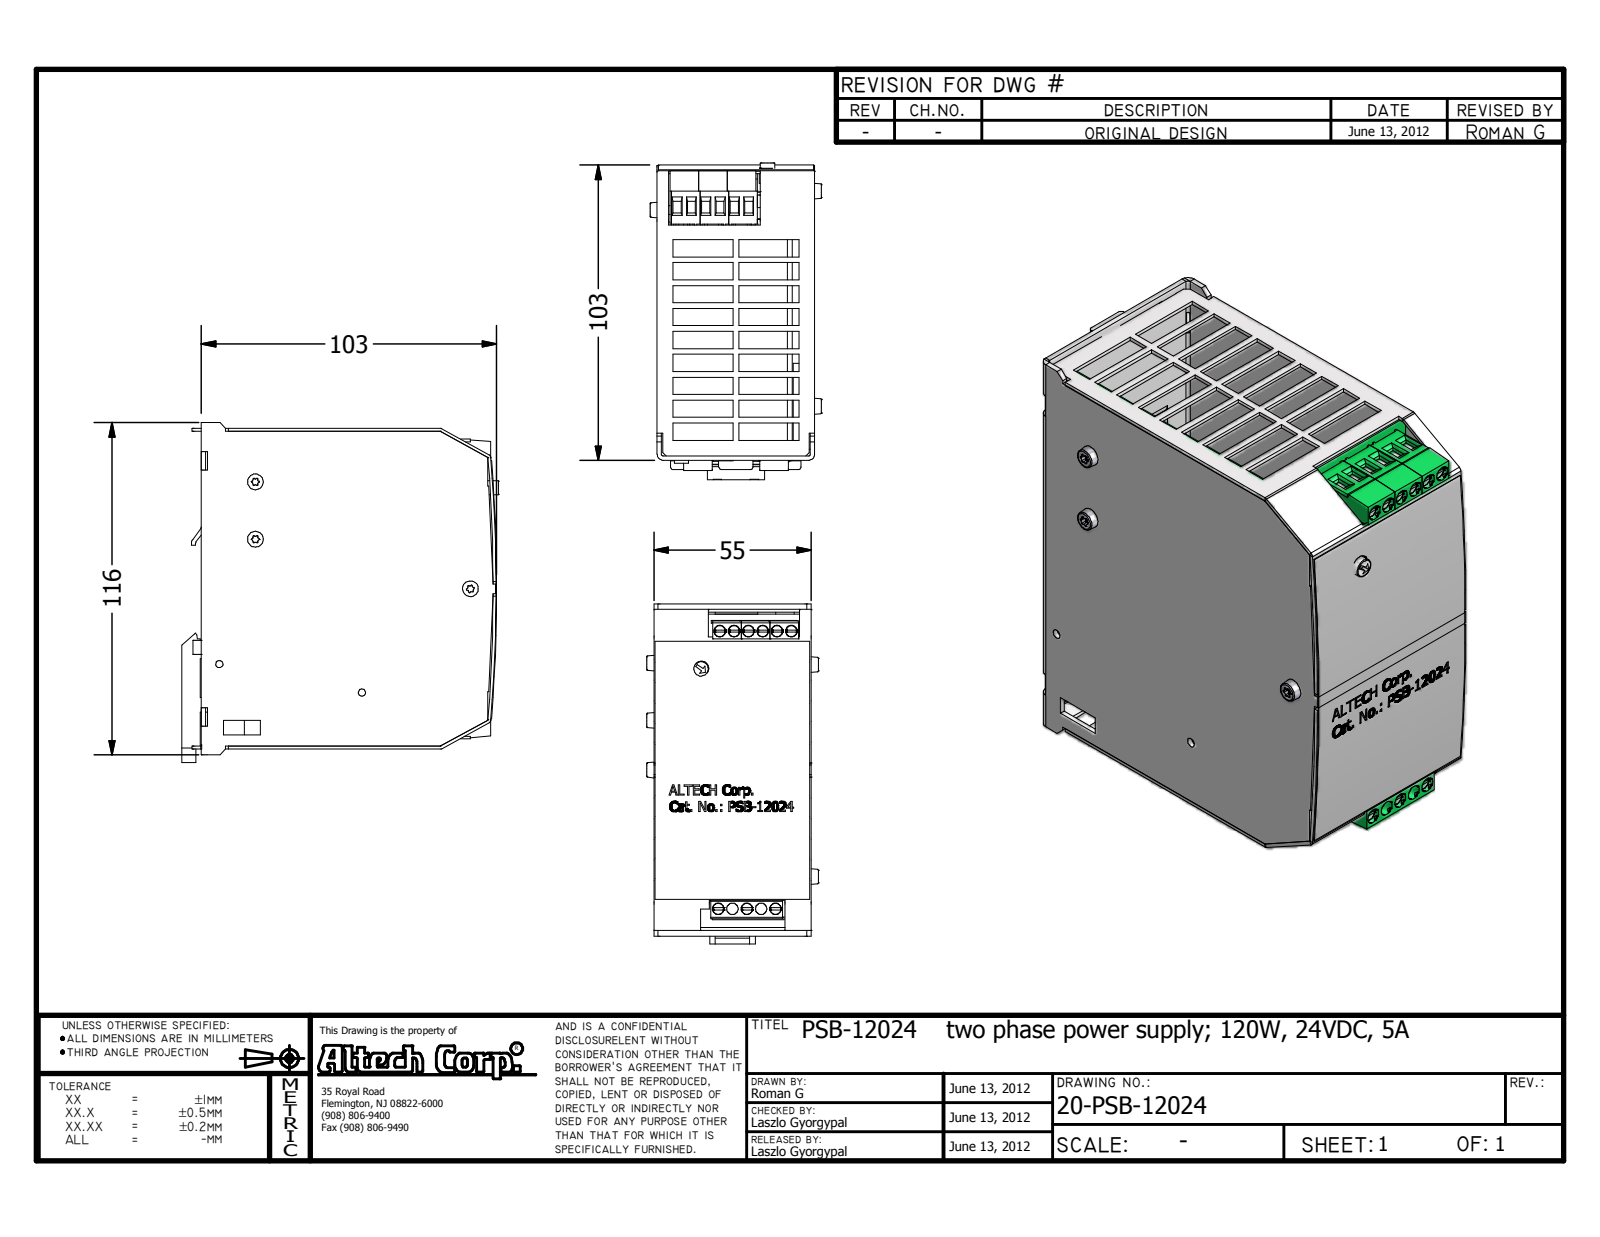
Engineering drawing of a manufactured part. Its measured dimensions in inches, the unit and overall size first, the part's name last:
Units: inches
Overall size (bounding box): 4.671 × 4.354 × 2.354
Round holes (diameter × count): ⌀0.039 ×38, ⌀0.157 ×11, ⌀0.035 ×4, ⌀0.091 ×4, ⌀0.11 ×3, ⌀0.13 ×3, ⌀0.079 ×2, ⌀0.098 ×2, ⌀0.122 ×2
Round bosses / shafts (diameter × count): ⌀0.152 ×9, ⌀0.055 ×9, ⌀0.118 ×5, ⌀0.105 ×5, ⌀0.185 ×2, ⌀0.06 ×2, ⌀0.354 ×1, ⌀0.197 ×1
Partial cylindrical surfaces — rounded edges, fillets, slot ends (radius × count): R0.004 ×46, R0.01 ×31, R0.022 ×30, R0.02 ×17, R0.008 ×16, R0.047 ×12, R0.039 ×8, R0.059 ×8
Main face-to-face distances: 0.059, 2.106, 0.063, 2.165, 0.315, 0.311, 1.795, 1.854, 0.374, 1.732
Hole centre spacings: 0.197, 0.1, 3.716, 0.394, 0.591, 3.817, 3.821, 3.823
Volume: 5.765 in³ · Surface area: 183.7 in²
Bodies: 1 solid, 2157 faces (1523 planar, 400 cylindrical, 234 other)
Part name (STEP PRODUCT): ALTECH-PSB-12024
STEP written by: Autodesk Inventor 2013 (CONFIG_CONTROL_DESIGN)
